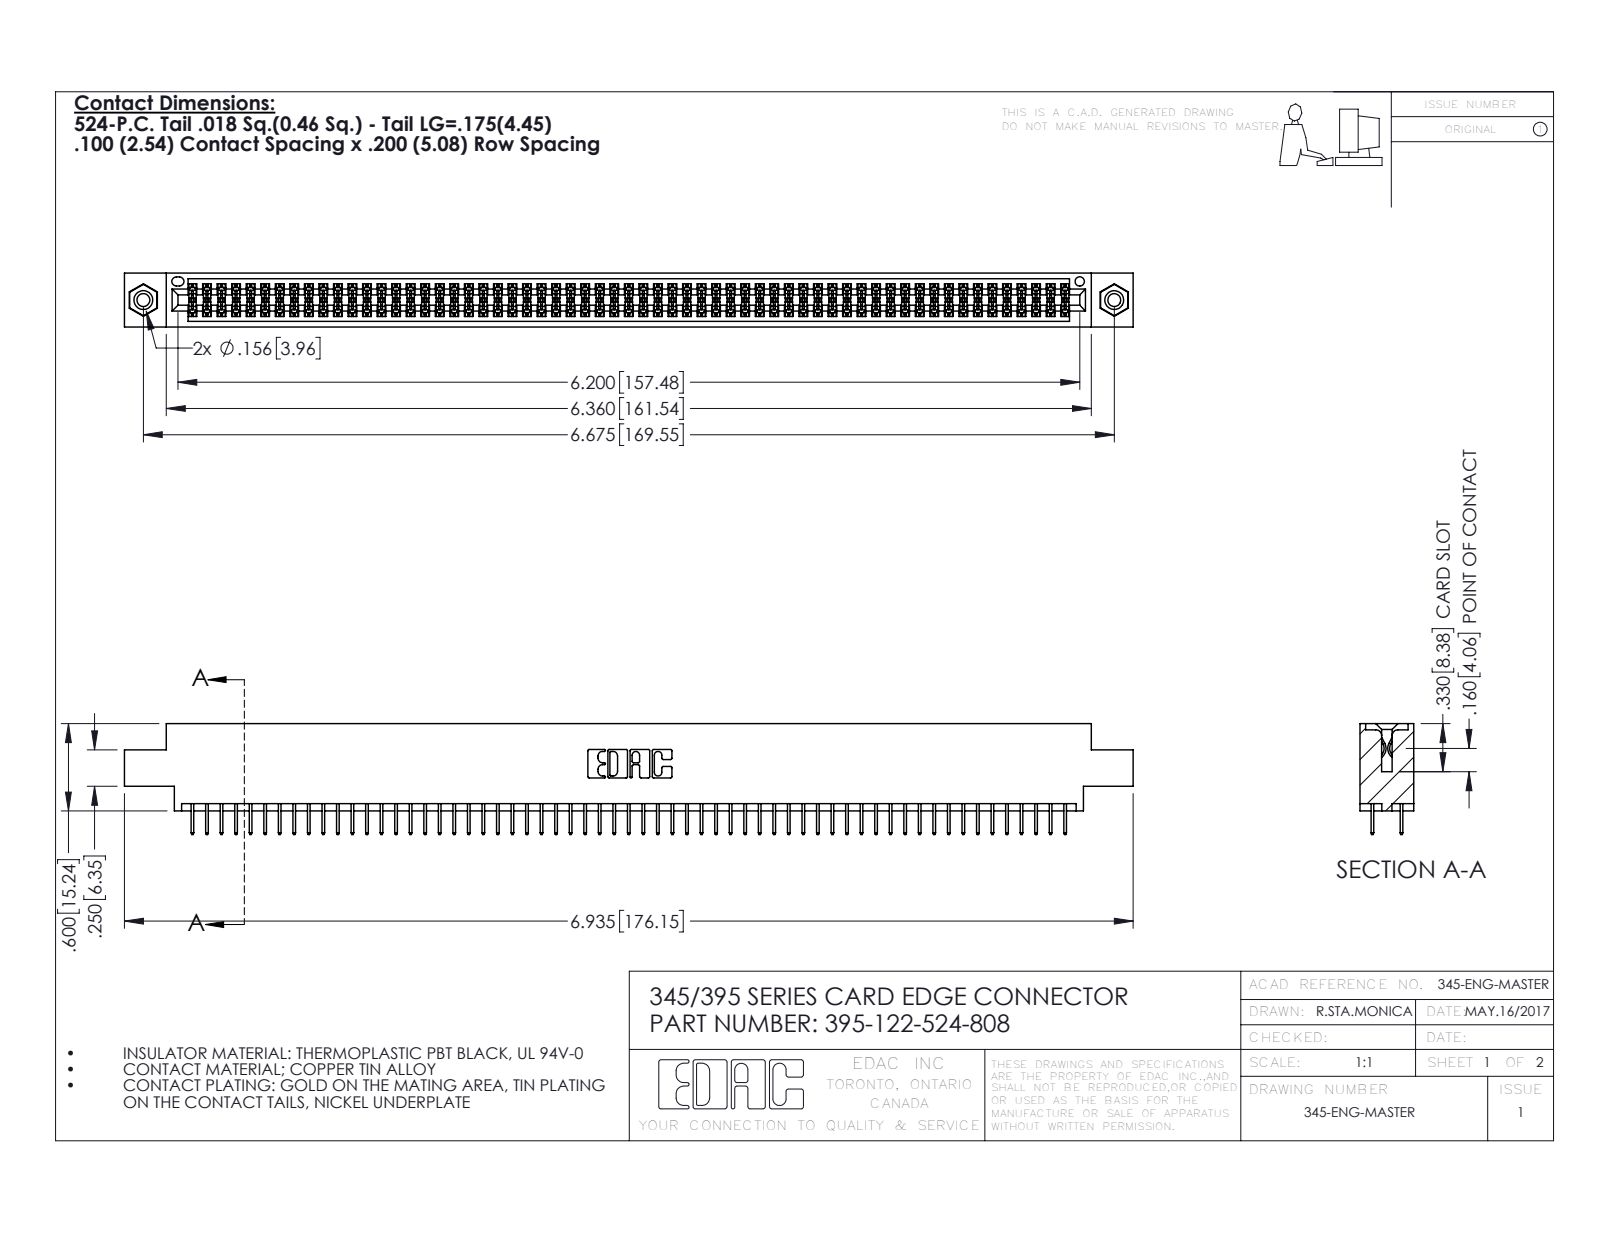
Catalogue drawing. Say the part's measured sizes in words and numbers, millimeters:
The part is named "395-122-524-808; 345-292-001_345-293-124; 345-250-001_345-250-003-102; 345 Part_0.170 Offset - 0.156 Dia-TI". Its 3-D file was written by "SolidWorks 2016 (CONFIG_CONTROL_DESIGN)". It is 125 solids with 6778 faces: 4874 planar, 1888 cylindrical and 16 other. Overall it measures 176.1 by 19.4 by 9.4 millimeters. Its volume is 16 980 cubic millimeters and its surface area 25 140 square millimeters. Round holes: 2 of diameter 2.3, 2 of diameter 3.2, 2 of diameter 4, 1 of diameter 1.6. Round bosses or shafts: 2 of diameter 3.9. Partial cylindrical surfaces (rounded edges, fillets, slot ends): 183 of radius 0.2, 22 of radius 0.3, 6 of radius 0.2, 6 of radius 0.8, 3 of radius 0.7, 2 of radius 0.4, 2 of radius 0.5, 2 of radius 0.6. The main face-to-face distances are 1.8, 7.6, 9.4, 5.1, 2.5, 6.9, 0.6, 5.7, 1.8, 4.4. The hole center spacings are 6.9, 163.6, 169.5.
